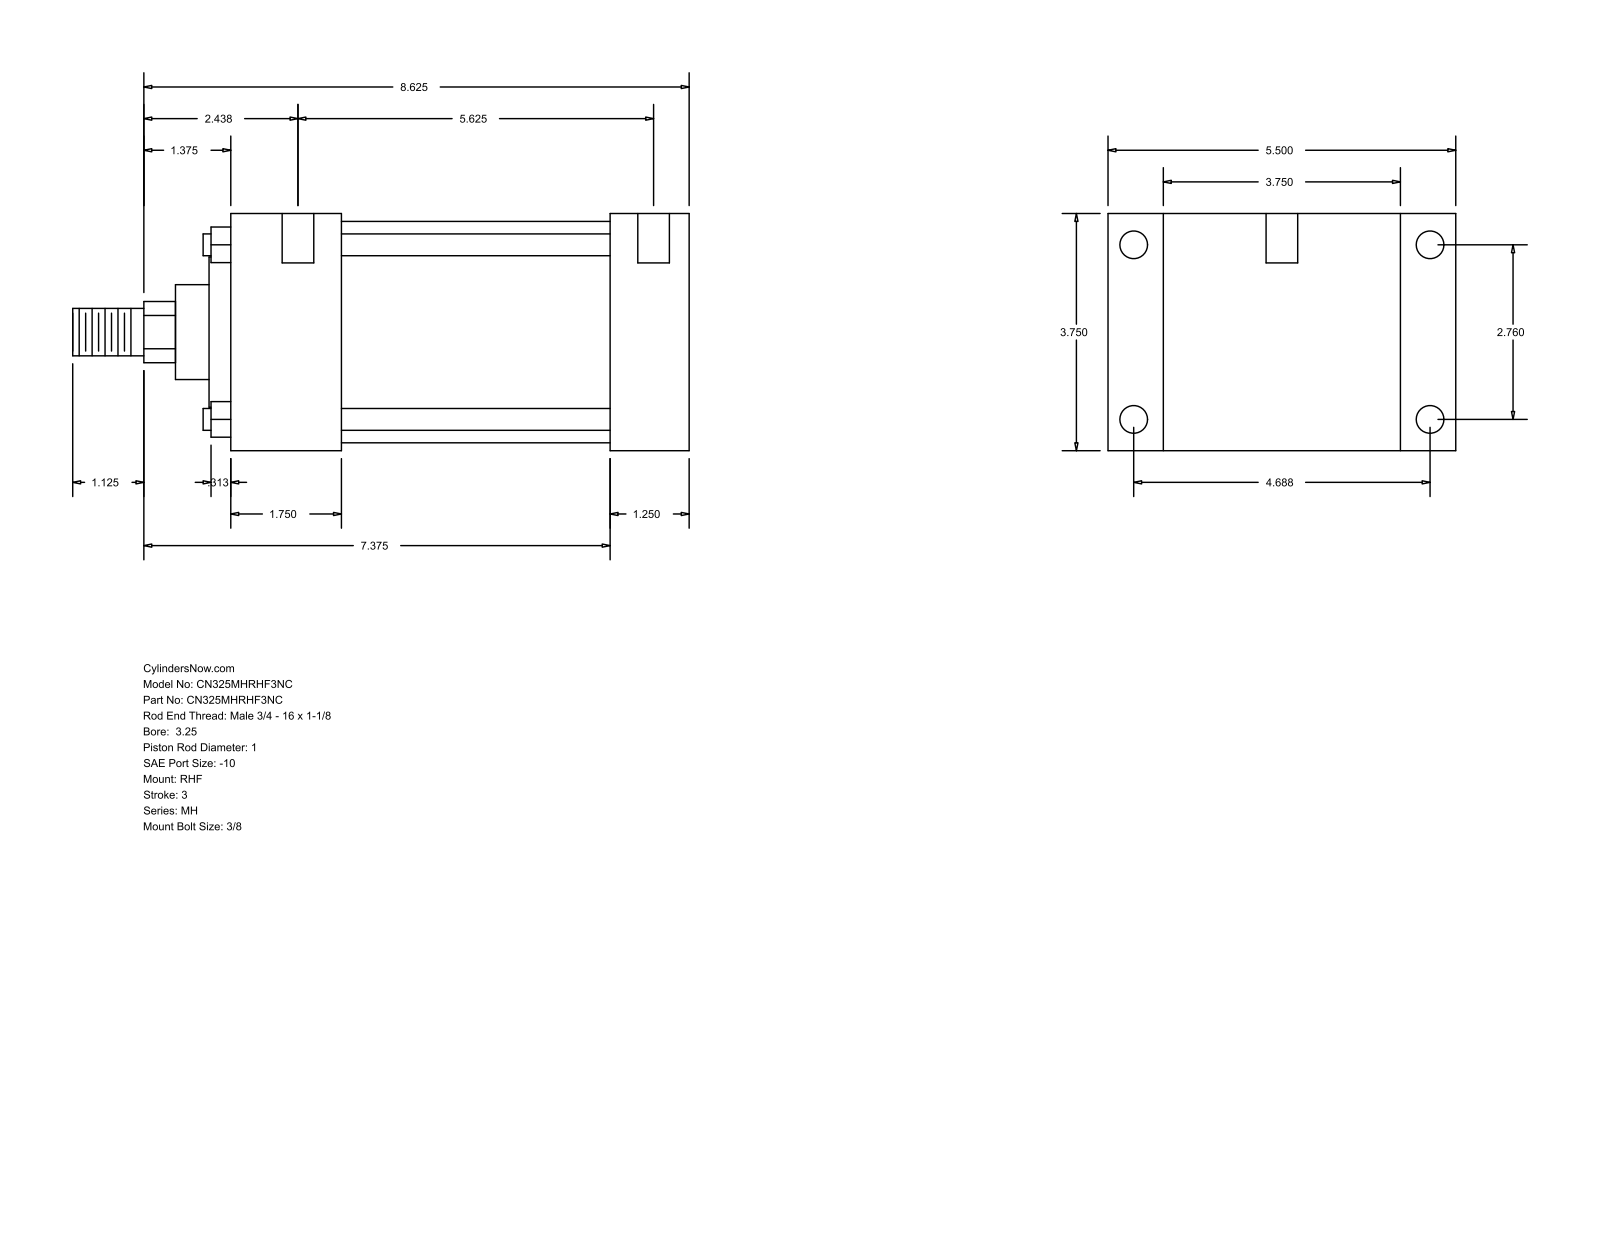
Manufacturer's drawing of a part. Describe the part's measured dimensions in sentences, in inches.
The part is named "MH_RHF__0325_1". Its 3-D file was written by "GSSL Pune (CONFIG_CONTROL_DESIGN)". It is 0 solids with 90 faces: 61 planar, 29 cylindrical and 0 other. Overall it measures 9.75 by 5.5 by 3.75 inches. Round holes: 4 of diameter 0.219, 4 of diameter 0.438, 2 of diameter 0.5. Round bosses or shafts: 4 of diameter 0.345, 1 of diameter 3.5, 1 of diameter 2.375, 1 of diameter 1.5, 1 of diameter 1, 1 of diameter 0.75. Partial cylindrical surfaces (rounded edges, fillets, slot ends): 1 of radius 0.484. The main face-to-face distances are 3.75, 1.25, 0.875, 4.625, 6, 7.25, 5.5, 1.75, 4.25, 5.5. The hole center spacings are 2.76, 4.687, 5.439, 5.875, 0.062, 0.187, 5.625, 5.687.
